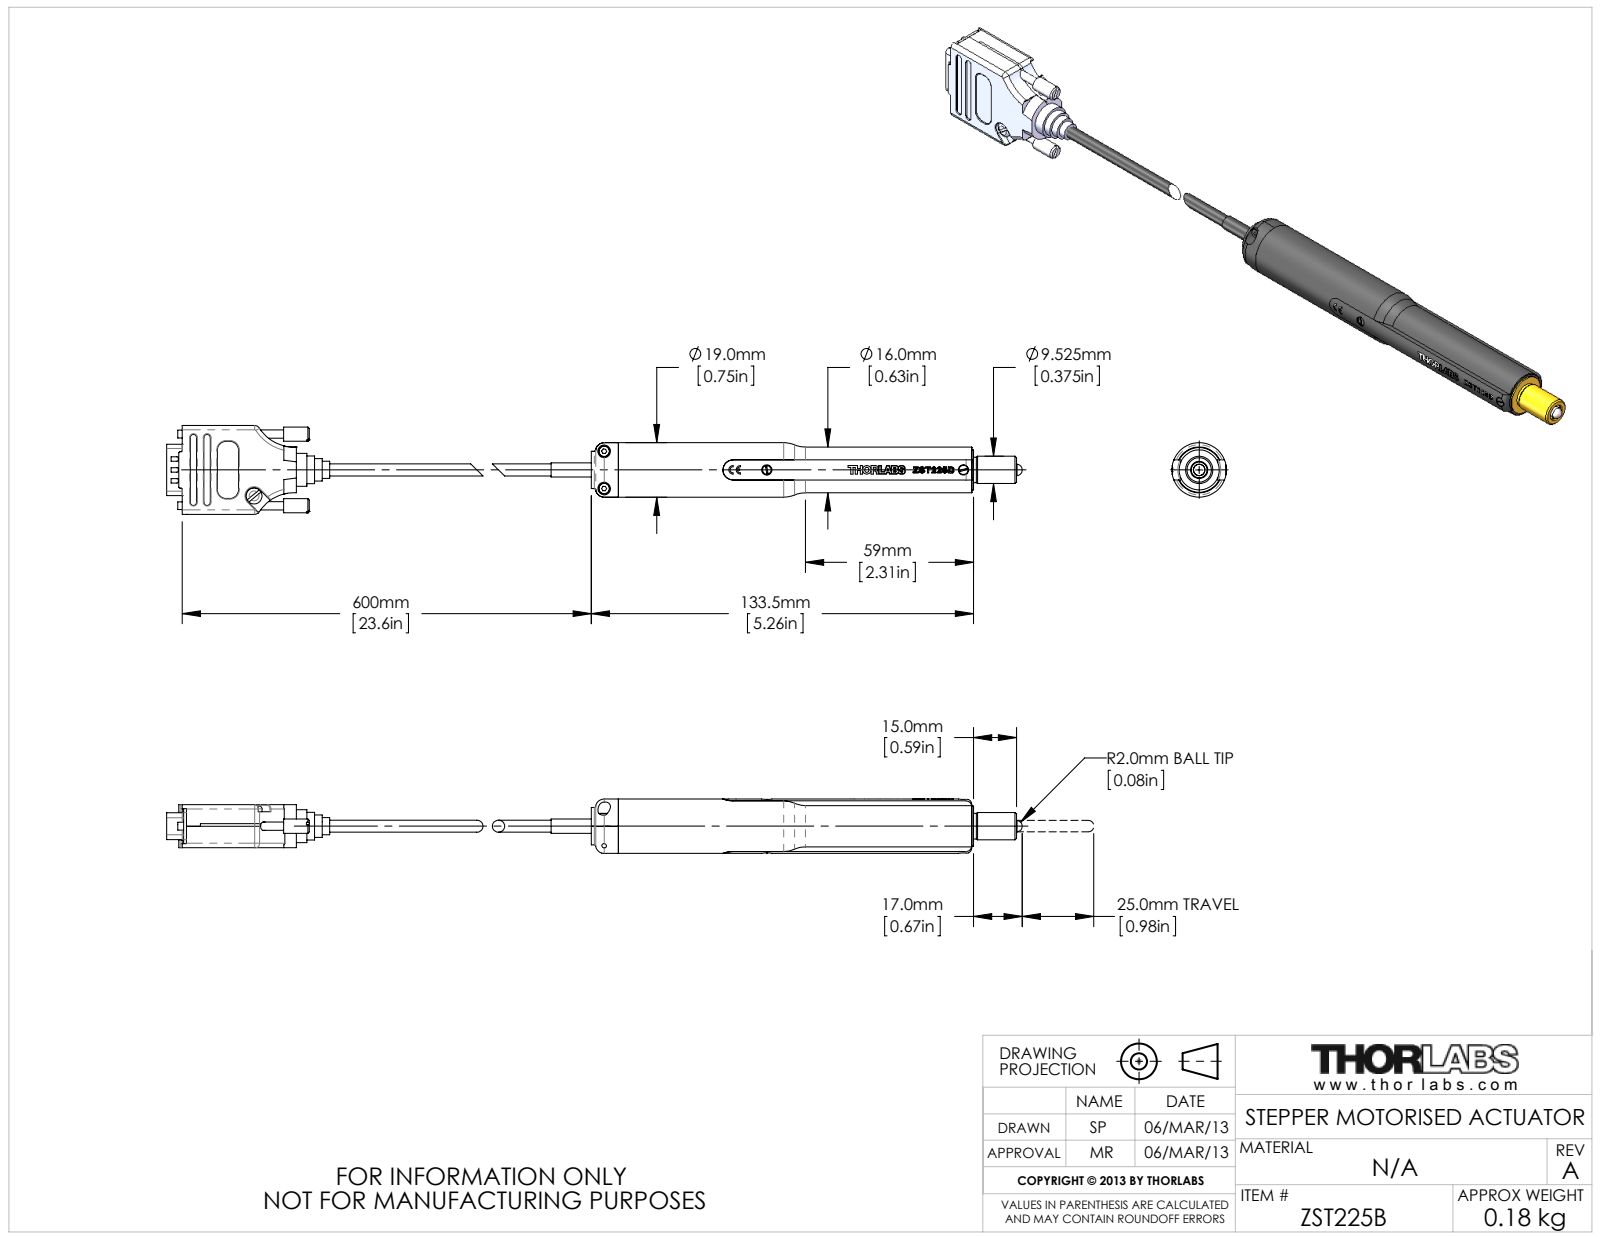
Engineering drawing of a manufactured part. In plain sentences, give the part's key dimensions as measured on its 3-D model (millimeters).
The part is named "ZST225B". Its 3-D file was written by "SolidWorks 2012 (AUTOMOTIVE_DESIGN)". It is 0 solids with 517 faces: 174 planar, 223 cylindrical and 120 other. Overall it measures 298.78 by 31 by 19 millimeters. Round holes: 3 of diameter 1.6, 2 of diameter 3.05, 2 of diameter 3.6, 2 of diameter 4.4, 1 of diameter 5.5. Round bosses or shafts: 15 of diameter 0.99, 2 of diameter 5.56, 2 of diameter 4.97, 2 of diameter 3.8, 2 of diameter 2.89, 2 of diameter 2.73, 1 of diameter 19, 1 of diameter 14. Partial cylindrical surfaces (rounded edges, fillets, slot ends): 24 of radius 0.25, 12 of radius 1.52, 5 of radius 0.51, 4 of radius 0.38, 4 of radius 1.1, 4 of radius 2.03, 4 of radius 3.05, 2 of radius 1.02. The main face-to-face distances are 1.39, 13.59, 12.2, 14.98, 12, 19, 0.35, 14.63, 1.04, 13.24. The hole center spacings are 6.5, 12.5, 57.17, 125.67, 13, 25, 56.8, 68.7.
